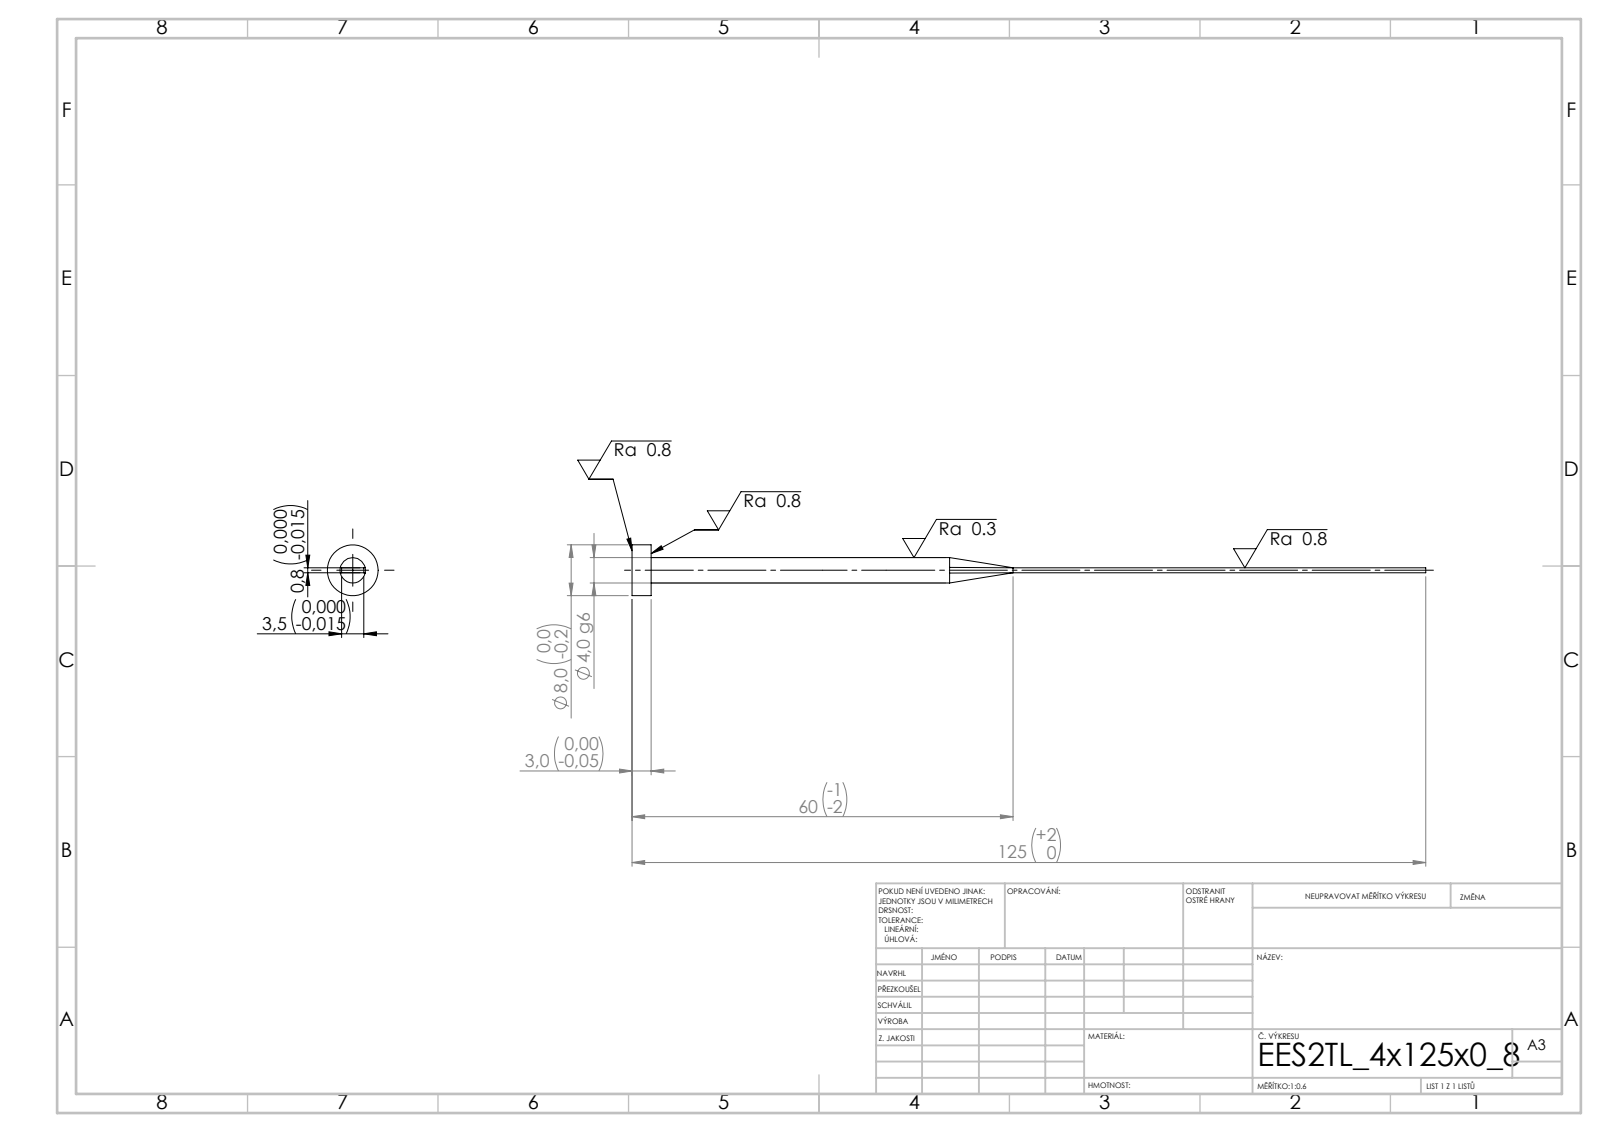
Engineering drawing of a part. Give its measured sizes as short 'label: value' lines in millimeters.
written by: SolidWorks 2019 (CONFIG_CONTROL_DESIGN)
unit: mm
bodies: 1 solid, 15 faces (7 planar, 4 cylindrical, 4 other)
size: 125 × 8 × 8
volume: 996 mm³; area: 1 418 mm²
bosses: 1× ⌀8, 1× ⌀4
face distances: 0.8, 3.5, 3, 125, 122
